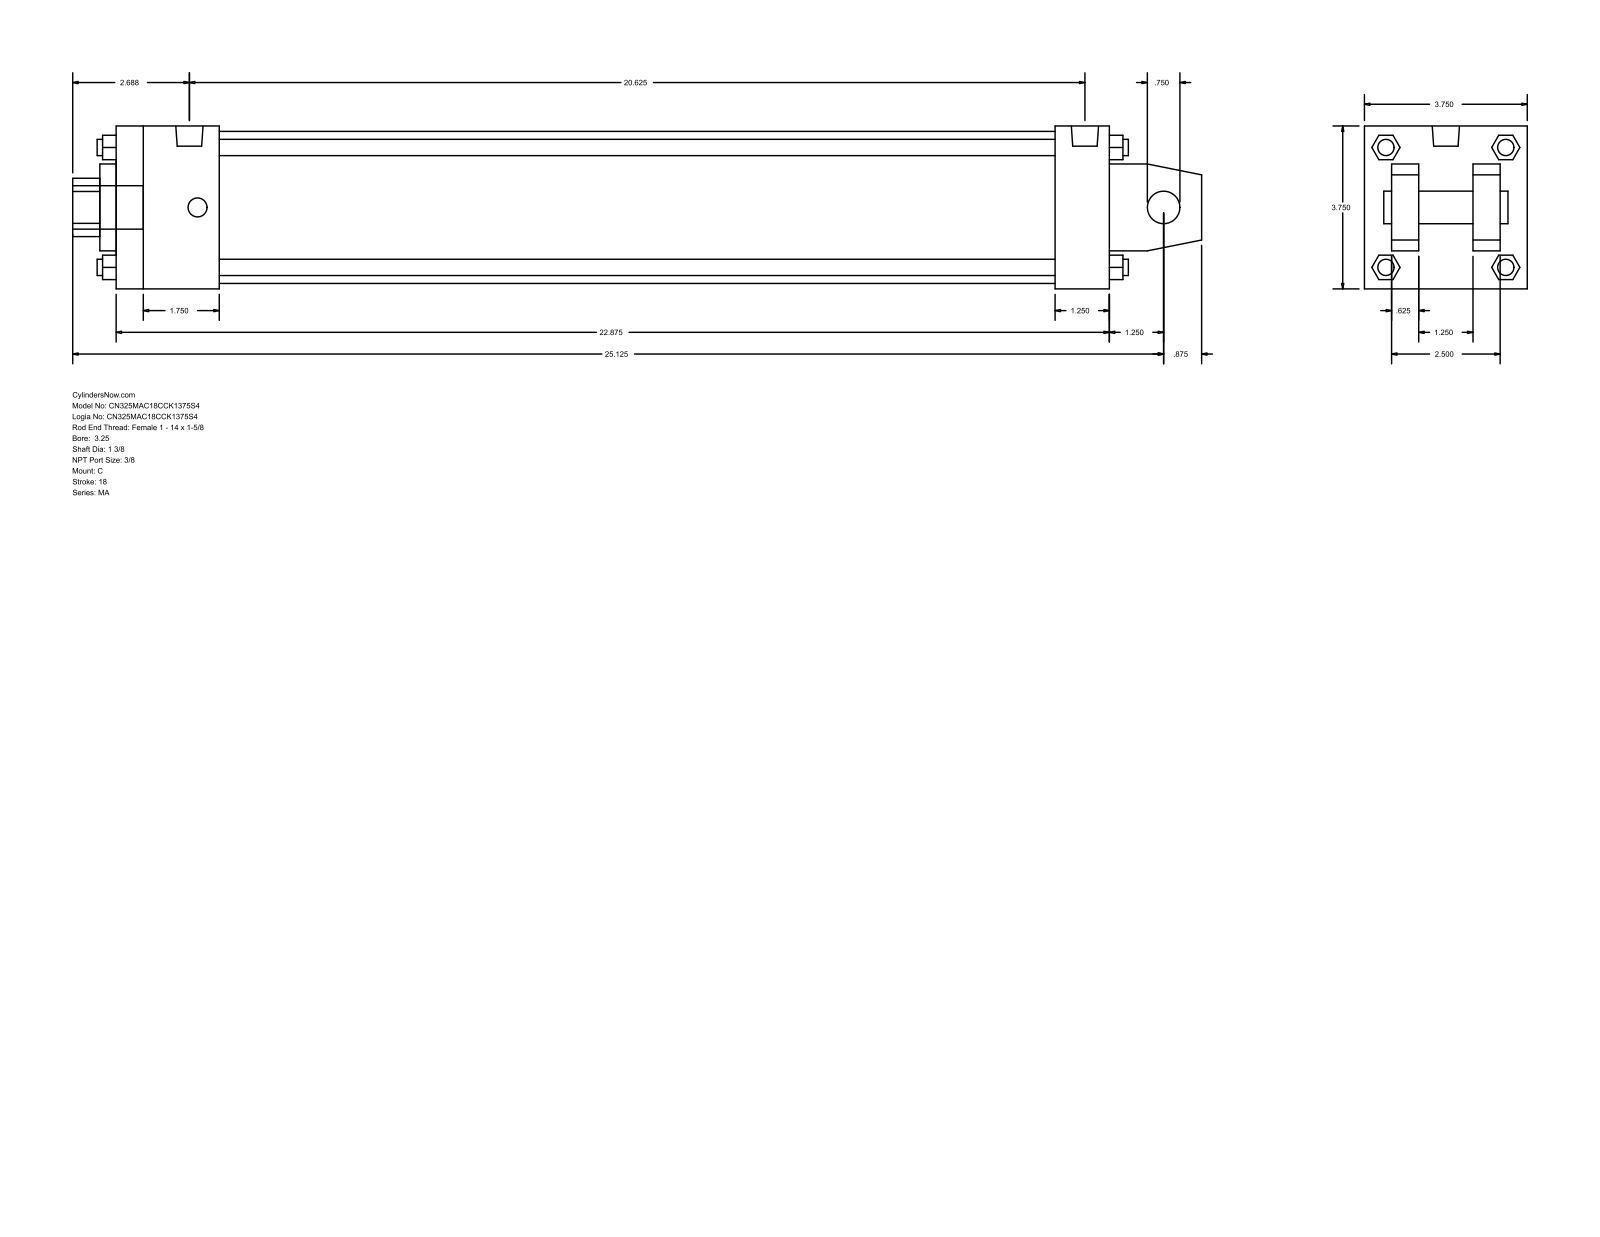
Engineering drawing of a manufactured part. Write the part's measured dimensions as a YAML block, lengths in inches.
part_name: "MA_C__0325_1.375"
step_written_by: "GSSL Pune (CONFIG_CONTROL_DESIGN)"
units: inches
bodies: {solids: 0, faces: 139, planar: 108, cylindrical: 31, other: 0}
overall_size: [26, 3.75, 3.75]
round_holes:
  - {diameter: 0.75, count: 1}
  - {diameter: 1.375, count: 1}
  - {diameter: 2, count: 1}
  - {diameter: 3.5, count: 1}
round_bosses_or_shafts:
  - {diameter: 0.437, count: 4}
  - {diameter: 0.375, count: 4}
  - {diameter: 0.627, count: 2}
  - {diameter: 1, count: 1}
partial_cylinders:
  - {radius: 0.672, count: 1}
face_to_face_distances: [3.75, 0.625, 2.5, 22.875, 1.25, 3.125, 1.875, 21.625, 1.25, 2.375]
